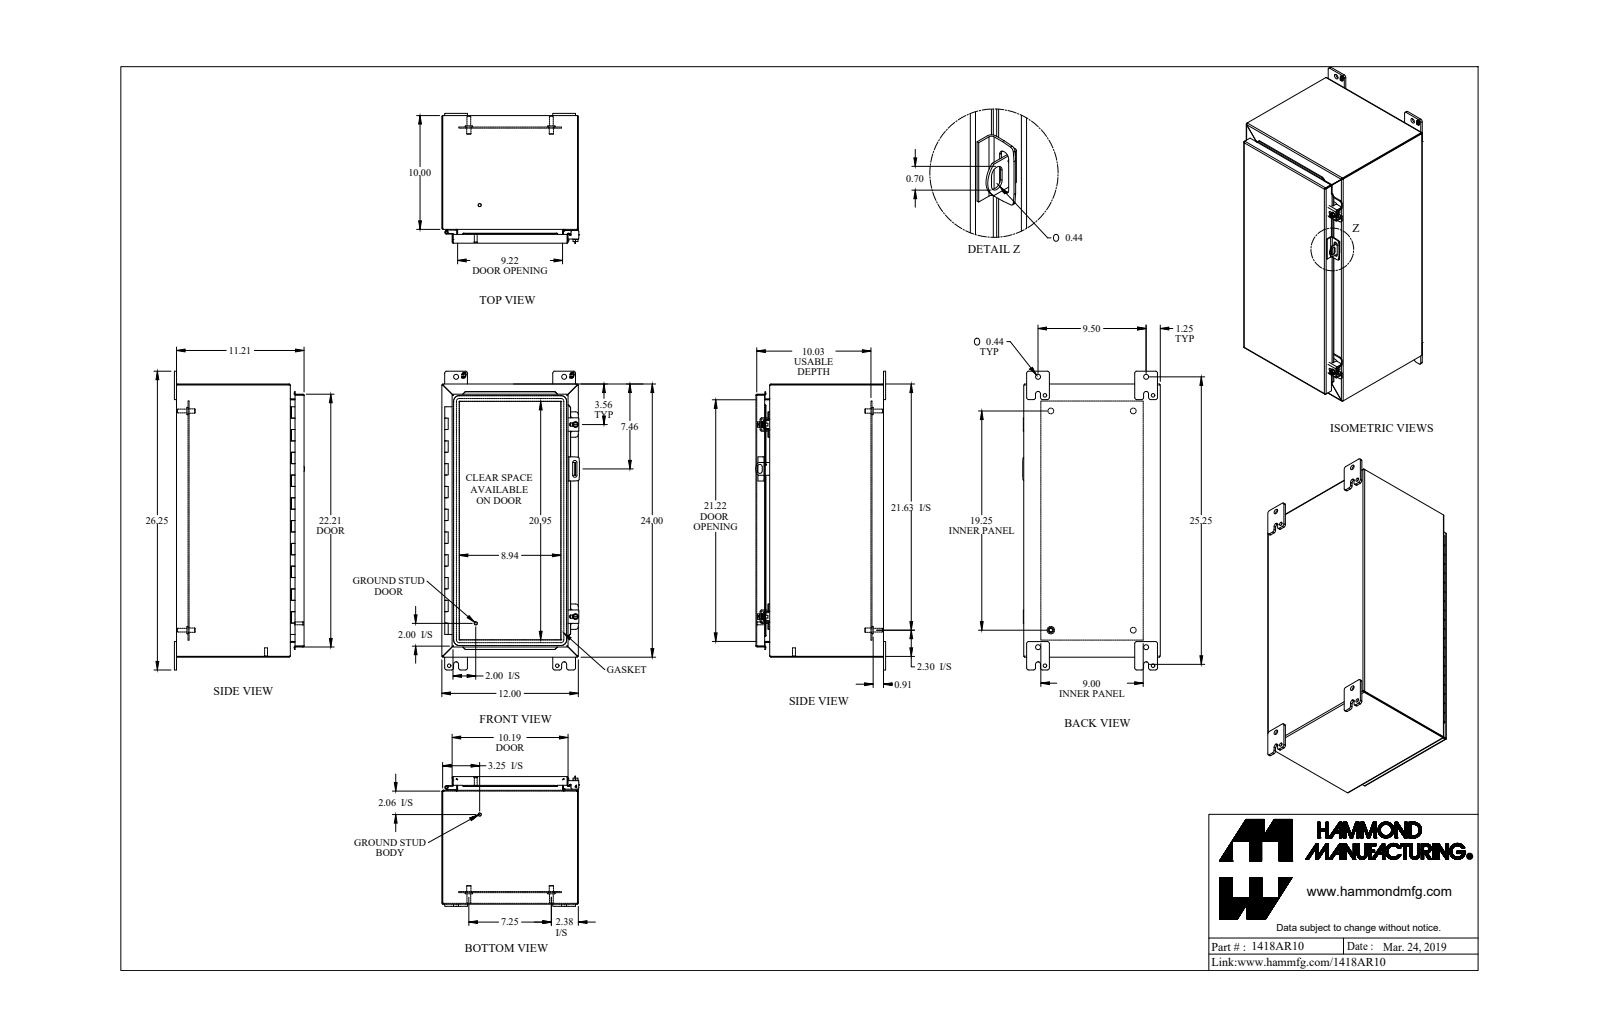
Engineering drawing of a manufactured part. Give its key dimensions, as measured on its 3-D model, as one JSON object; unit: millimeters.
{"part_name": "1418AR10", "step_written_by": "SolidWorks 2019 (AUTOMOTIVE_DESIGN)", "units": "millimeters", "bodies": {"solids": 38, "faces": 1003, "planar": 690, "cylindrical": 259, "other": 54}, "overall_size": [666.8, 307.2, 290.5], "volume_mm3": 2281000, "surface_area_mm2": 2358000, "round_holes": [[8, 4], [11.1, 4], [12.7, 4], [5.4, 2], [6.7, 2], [7.8, 2], [9.5, 2], [11.3, 2], [3.2, 1], [4.7, 1]], "round_bosses_or_shafts": [[16.5, 4], [9.5, 4], [8.4, 4], [25.4, 2], [12.7, 2], [9.9, 2], [7.1, 2], [6.4, 2]], "partial_cylinders_radius": [[4.8, 26], [0.9, 20], [2.7, 20], [1.2, 13], [3.6, 13], [0.2, 8], [1.1, 8], [2, 8]], "face_to_face_distances": [1.8, 282.3, 303, 280.4, 301.1, 304.8, 607.8, 284.1, 2.4, 256.1], "hole_center_spacings": [241.3, 489, 522.5, 44.1, 61.8, 522.5, 527.8, 568.4]}
